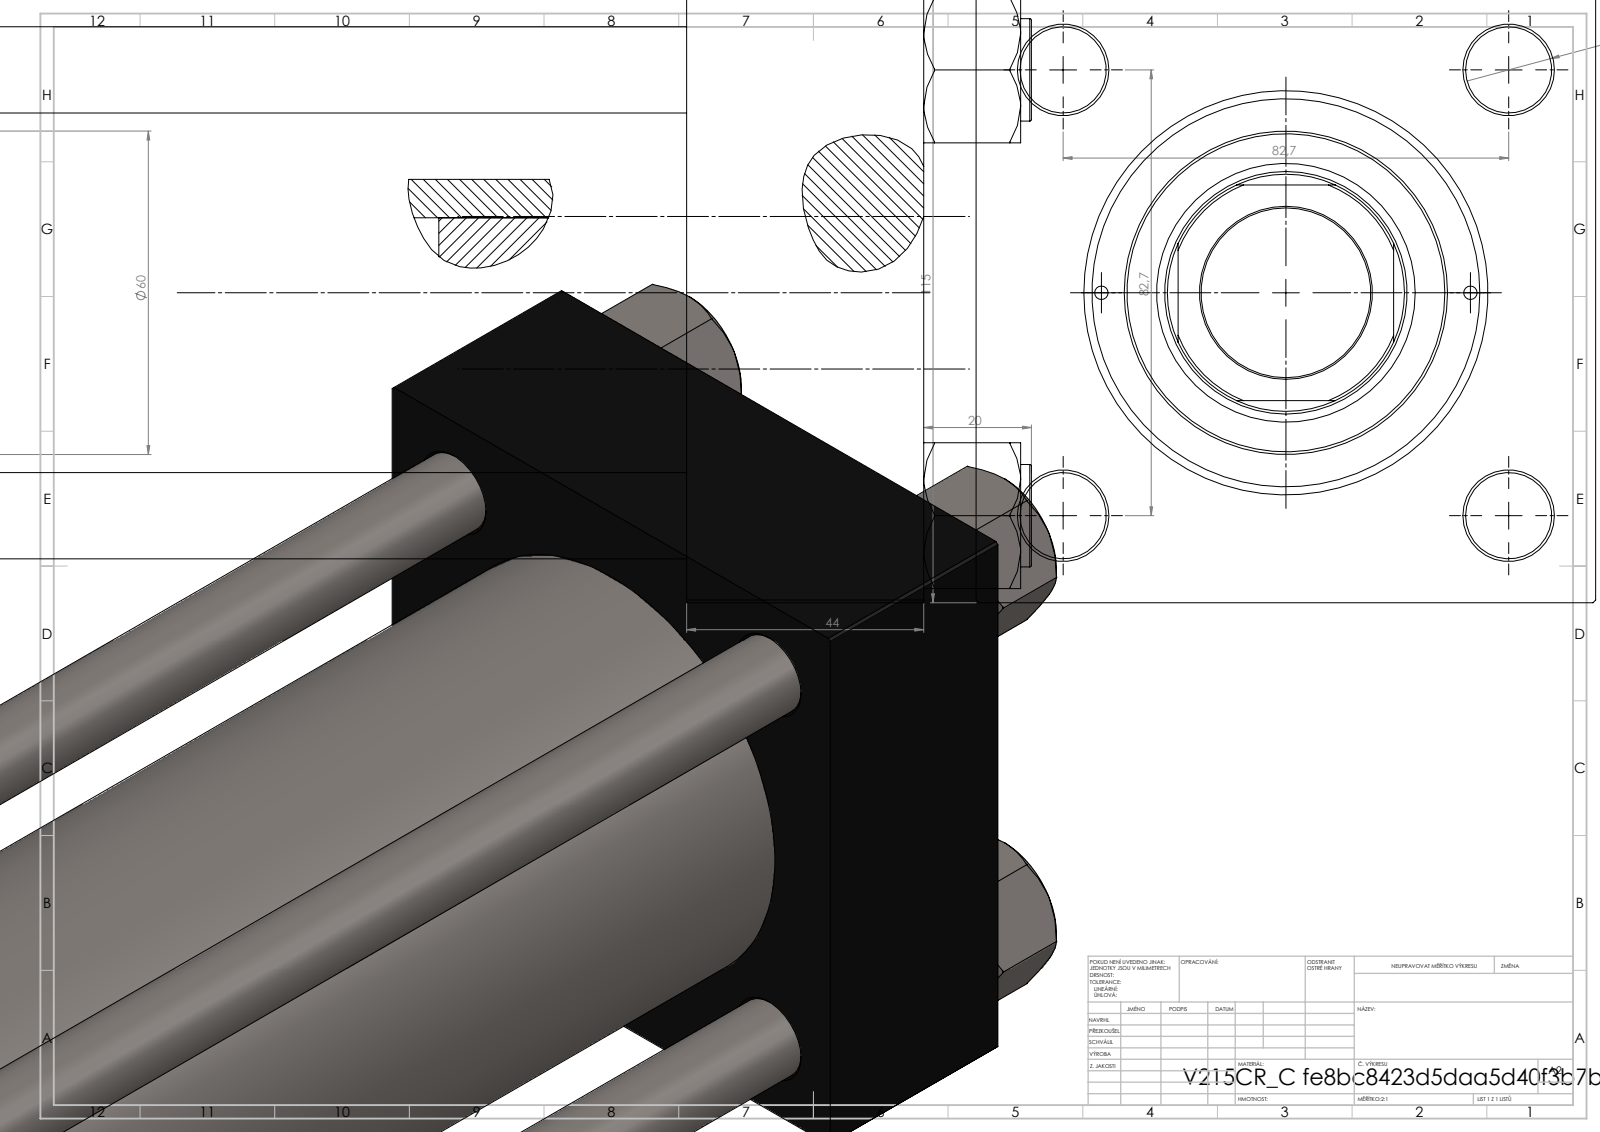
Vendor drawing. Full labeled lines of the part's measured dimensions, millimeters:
Part name (STEP PRODUCT): V215CR_C_Body; V215CR_C_TYCINKA; NUT_M5_C; V215CR_VCP_C (+1 more)
STEP written by: SolidWorks 2019 (CONFIG_CONTROL_DESIGN)
Units: millimetres
Bodies: 11 solids, 1202 faces (576 planar, 90 cylindrical, 536 other)
Overall size (bounding box): 560 × 115 × 115
Volume: 2 868 000 mm³ · Surface area: 559 054 mm²
Round holes (diameter × count): ⌀16 ×4, ⌀2.5 ×2, ⌀7 ×2, ⌀26.44 ×2, ⌀35 ×2, ⌀31.5 ×1, ⌀45 ×1, ⌀48 ×1, ⌀61 ×1, ⌀72 ×1, ⌀80 ×1
Round bosses / shafts (diameter × count): ⌀19 ×4, ⌀86 ×1, ⌀60 ×1
Partial cylindrical surfaces — rounded edges, fillets, slot ends (radius × count): R22 ×1
Main face-to-face distances: 115, 44, 509, 465, 440, 396, 69, 480.3, 436.3, 40.3
Hole centre spacings: 41.96, 58.48, 82.7, 86.17, 34.25, 116.96, 68.5, 441
